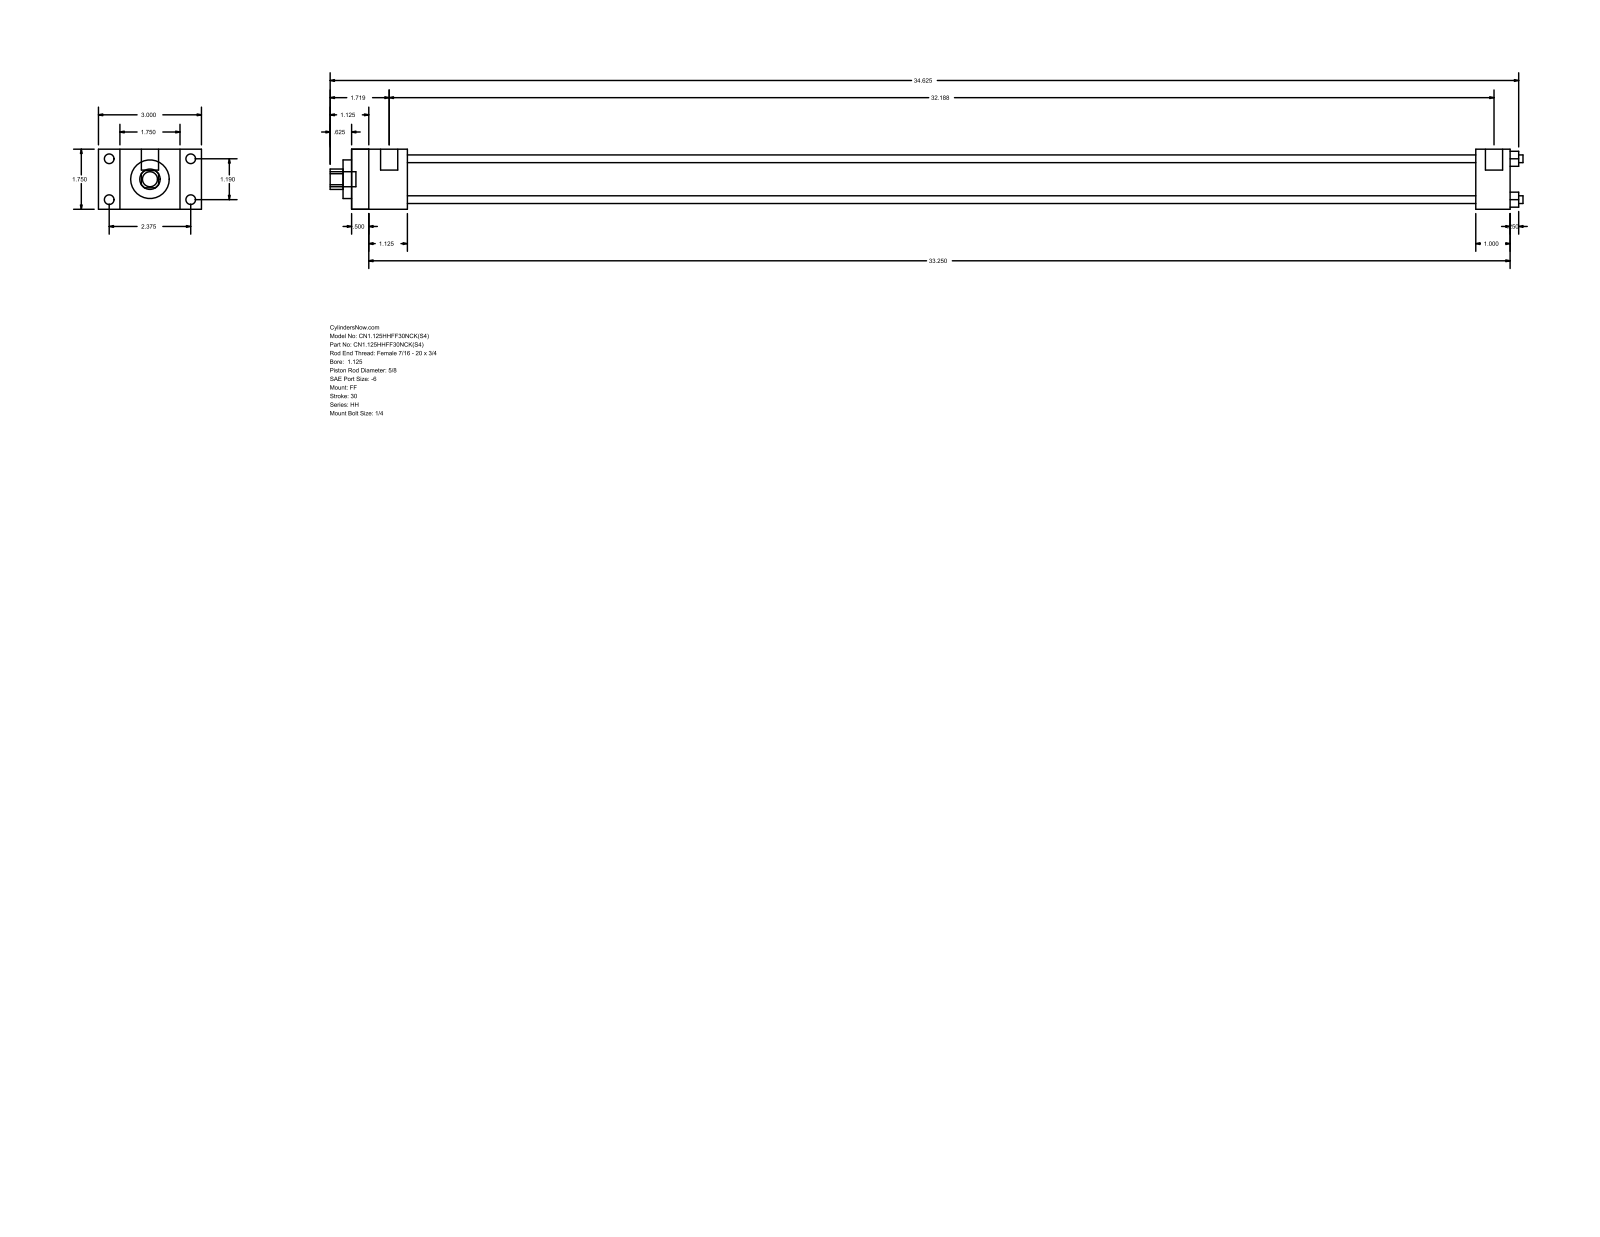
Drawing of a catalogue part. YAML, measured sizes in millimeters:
part_name: "HH_FF__0112_0.625"
step_written_by: "GSSL Pune (CONFIG_CONTROL_DESIGN)"
units: millimeters
bodies: {solids: 0, faces: 92, planar: 64, cylindrical: 28, other: 0}
overall_size: [882.65, 76.2, 44.45]
round_holes:
  - {diameter: 5.71, count: 4}
  - {diameter: 15.88, count: 1}
  - {diameter: 28.57, count: 1}
  - {diameter: 34.92, count: 1}
round_bosses_or_shafts:
  - {diameter: 7.14, count: 4}
  - {diameter: 5.56, count: 4}
  - {diameter: 12.7, count: 2}
  - {diameter: 11.11, count: 1}
partial_cylinders:
  - {radius: 7.54, count: 1}
face_to_face_distances: [44.46, 857.24, 15.87, 12.69, 844.55, 60.33, 28.58, 41.27, 831.85, 819.16]
hole_center_spacings: [21.37, 30.22, 42.74]
